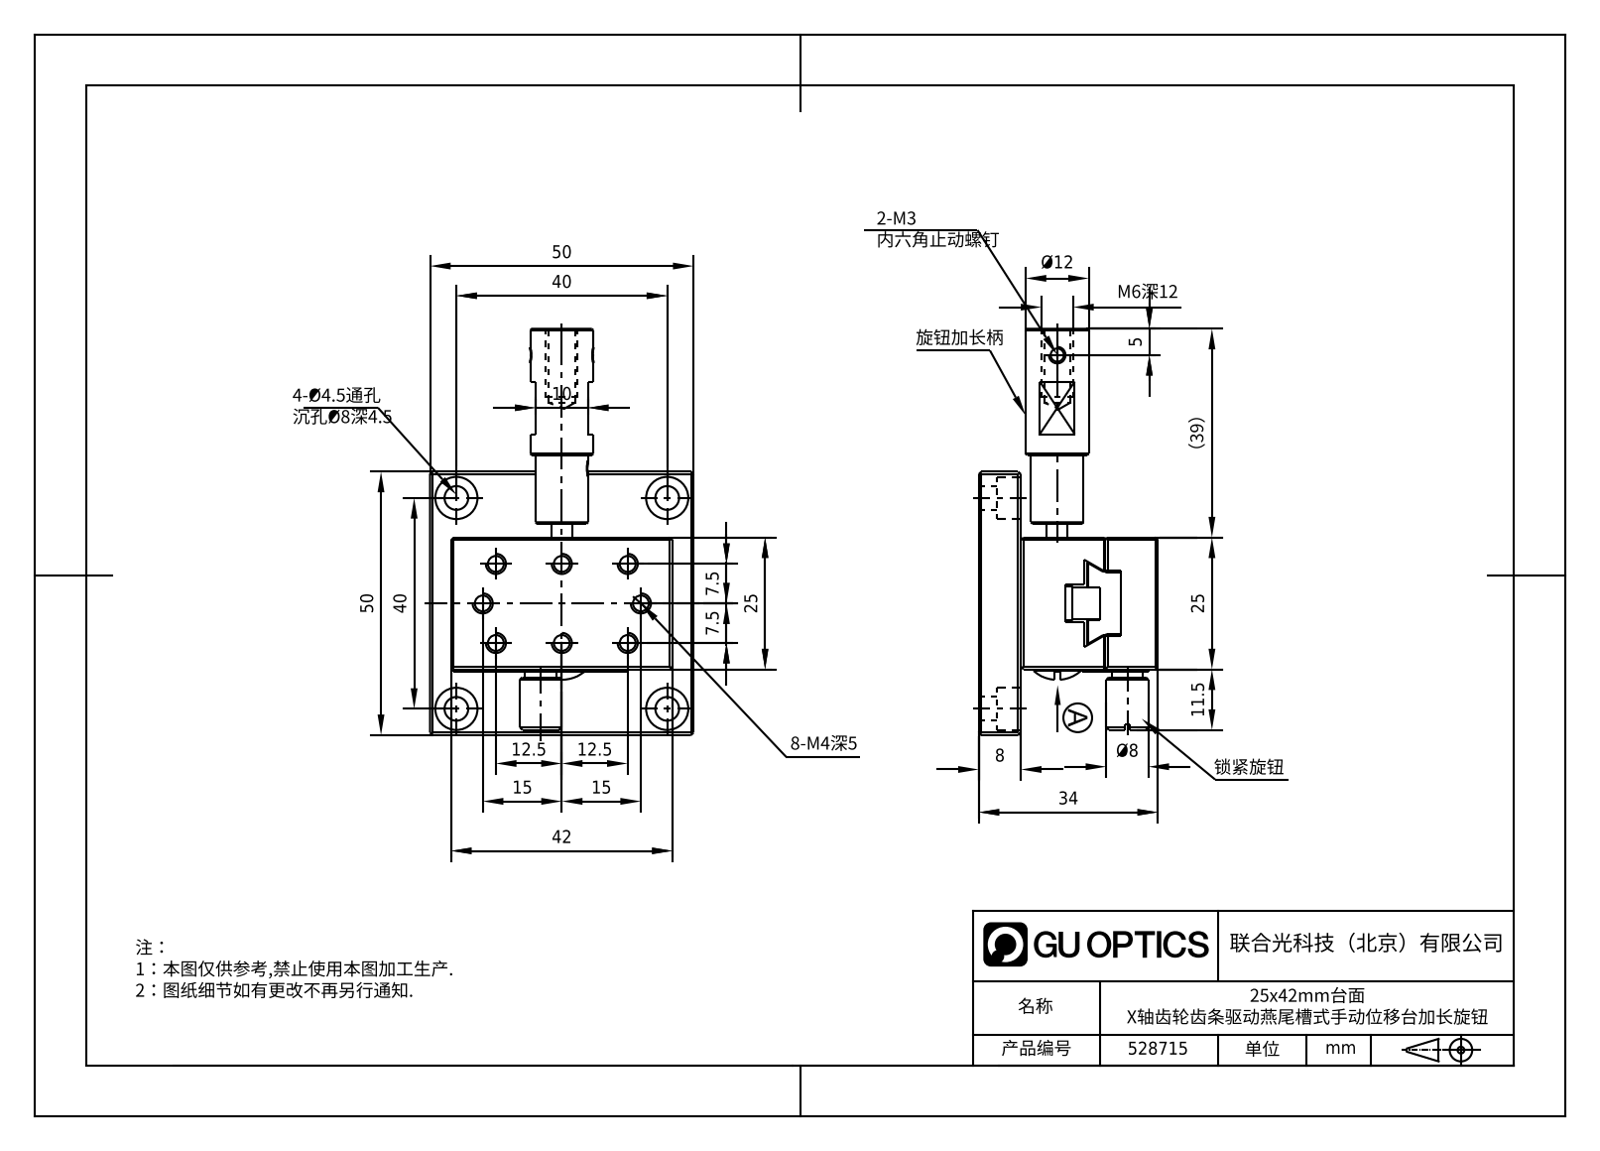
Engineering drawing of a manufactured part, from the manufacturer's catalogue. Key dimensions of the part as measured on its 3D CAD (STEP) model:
Part name (STEP PRODUCT): 528715
STEP written by: SolidWorks 2020 (CONFIG_CONTROL_DESIGN)
Units: millimetres
Bodies: 0 solids, 306 faces (181 planar, 68 cylindrical, 57 other)
Overall size (bounding box): 76.5 × 50 × 34
Round holes (diameter × count): ⌀3.24 ×10, ⌀4.5 ×6, ⌀2.01 ×4, ⌀2.46 ×4, ⌀8 ×4, ⌀4 ×3, ⌀1.57 ×2, ⌀2.2 ×2, ⌀2.6 ×2, ⌀2.8 ×2, ⌀5 ×2, ⌀7.5 ×2
Round bosses / shafts (diameter × count): ⌀8 ×2, ⌀10 ×1, ⌀9 ×1, ⌀6.5 ×1, ⌀6 ×1, ⌀5.83 ×1, ⌀3.5 ×1, ⌀3 ×1
Partial cylindrical surfaces — rounded edges, fillets, slot ends (radius × count): R2 ×4, R1.8 ×2
Main face-to-face distances: 8, 7, 19, 4, 12.5, 10, 3, 27, 16, 25
Hole centre spacings: 34, 23.58, 28.5, 40, 7.65, 7.91, 8.75, 9.01
